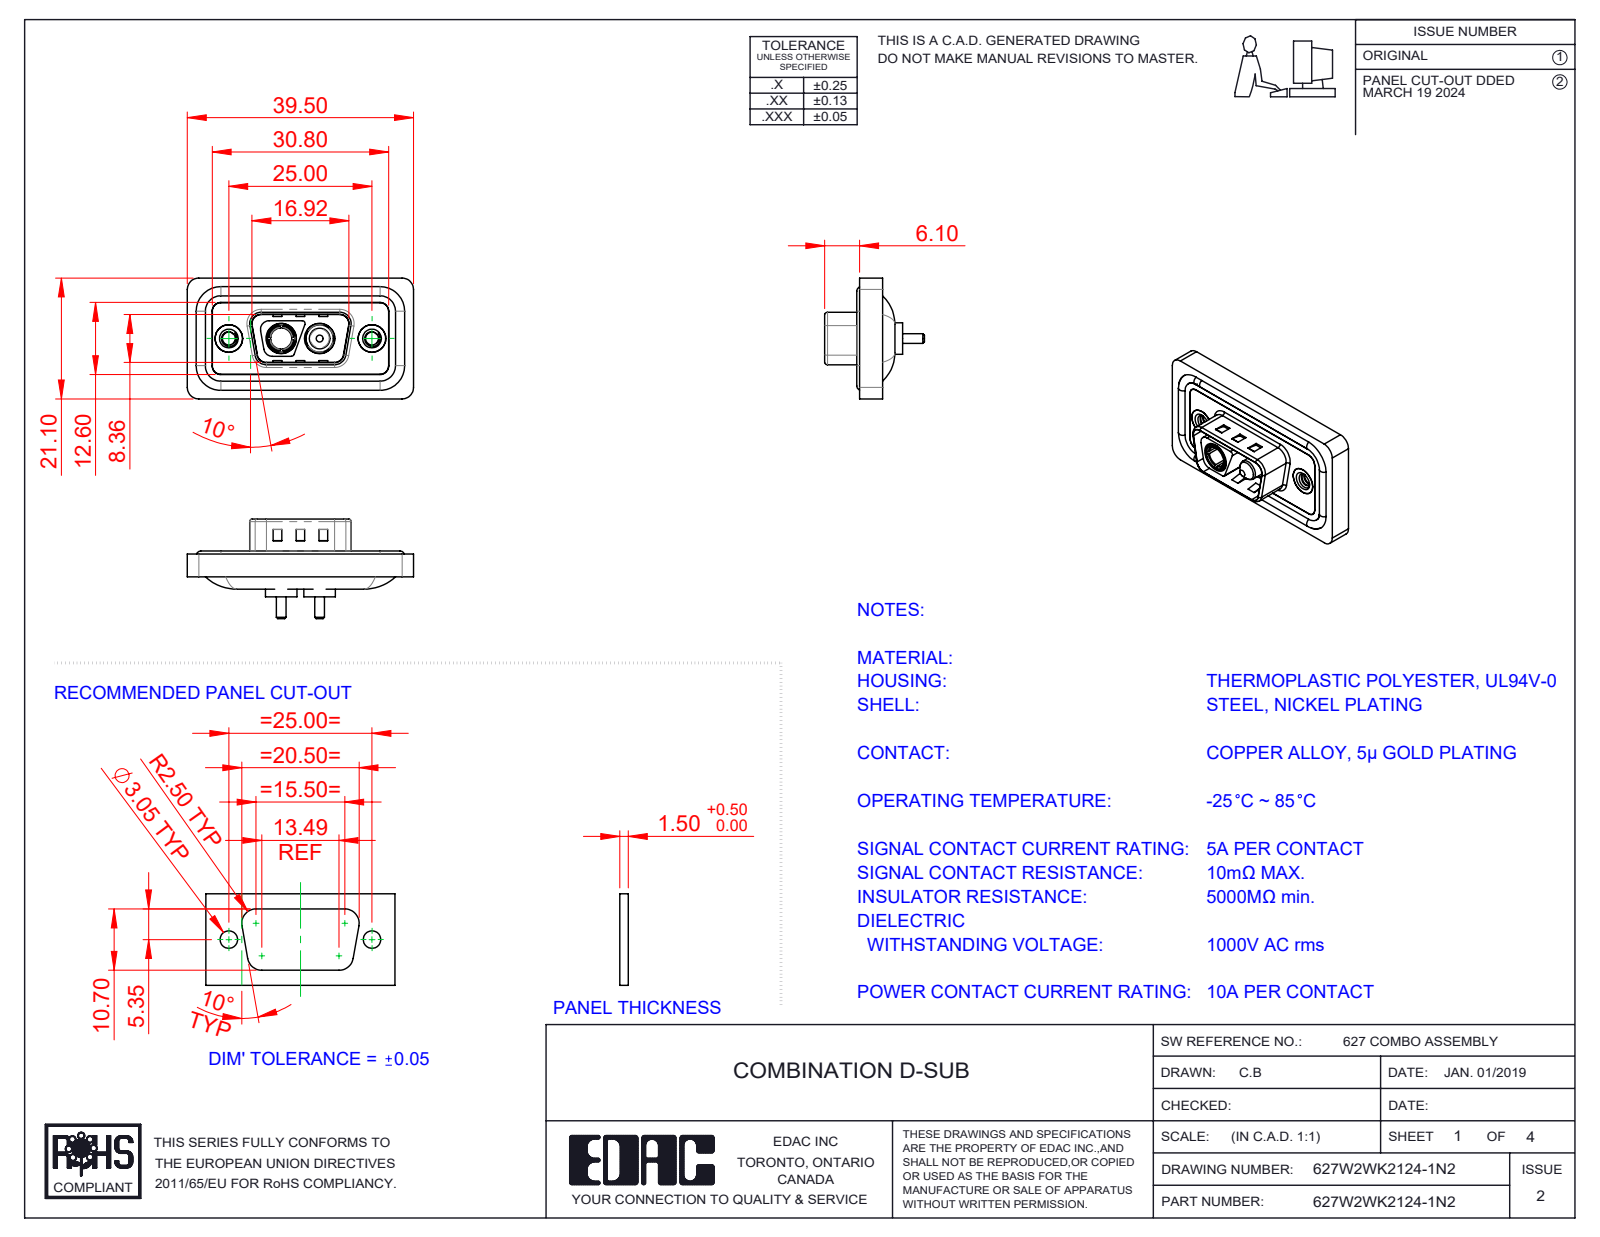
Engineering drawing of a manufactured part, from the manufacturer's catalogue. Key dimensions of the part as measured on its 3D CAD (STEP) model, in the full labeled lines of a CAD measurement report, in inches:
Part name (STEP PRODUCT): 627W2WK2124-1N2; Power Pin_10A S; 627Combo Housing_2WK2; 627Combo Shell Rear_09 Contacts (+4 more)
STEP written by: SolidWorks 2023 (CONFIG_CONTROL_DESIGN)
Units: inches
Bodies: 11 solids, 534 faces (189 planar, 227 cylindrical, 118 other)
Overall size (bounding box): 1.555 × 0.831 × 0.685
Volume: 0.276 in³ · Surface area: 11.34 in²
Round holes (diameter × count): ⌀0.089 ×2, ⌀0.157 ×2, ⌀0.189 ×2, ⌀0.191 ×2, ⌀0.197 ×2, ⌀0.209 ×2, ⌀0.146 ×1
Round bosses / shafts (diameter × count): ⌀0.063 ×4, ⌀0.217 ×2, ⌀0.205 ×2, ⌀0.193 ×2, ⌀0.187 ×2, ⌀0.148 ×2, ⌀0.067 ×2, ⌀0.195 ×1
Partial cylindrical surfaces — rounded edges, fillets, slot ends (radius × count): R0.059 ×24, R0.079 ×18, R0.02 ×10, R0.063 ×8, R0.01 ×4, R0.024 ×4, R0.026 ×4, R0.035 ×4
Main face-to-face distances: 0.016, 0.043, 0.114, 0.02, 0.122, 0.063, 0.059, 0.157, 0.098, 0.071
Hole centre spacings: 0.36, 0.624, 0.265, 0.984
